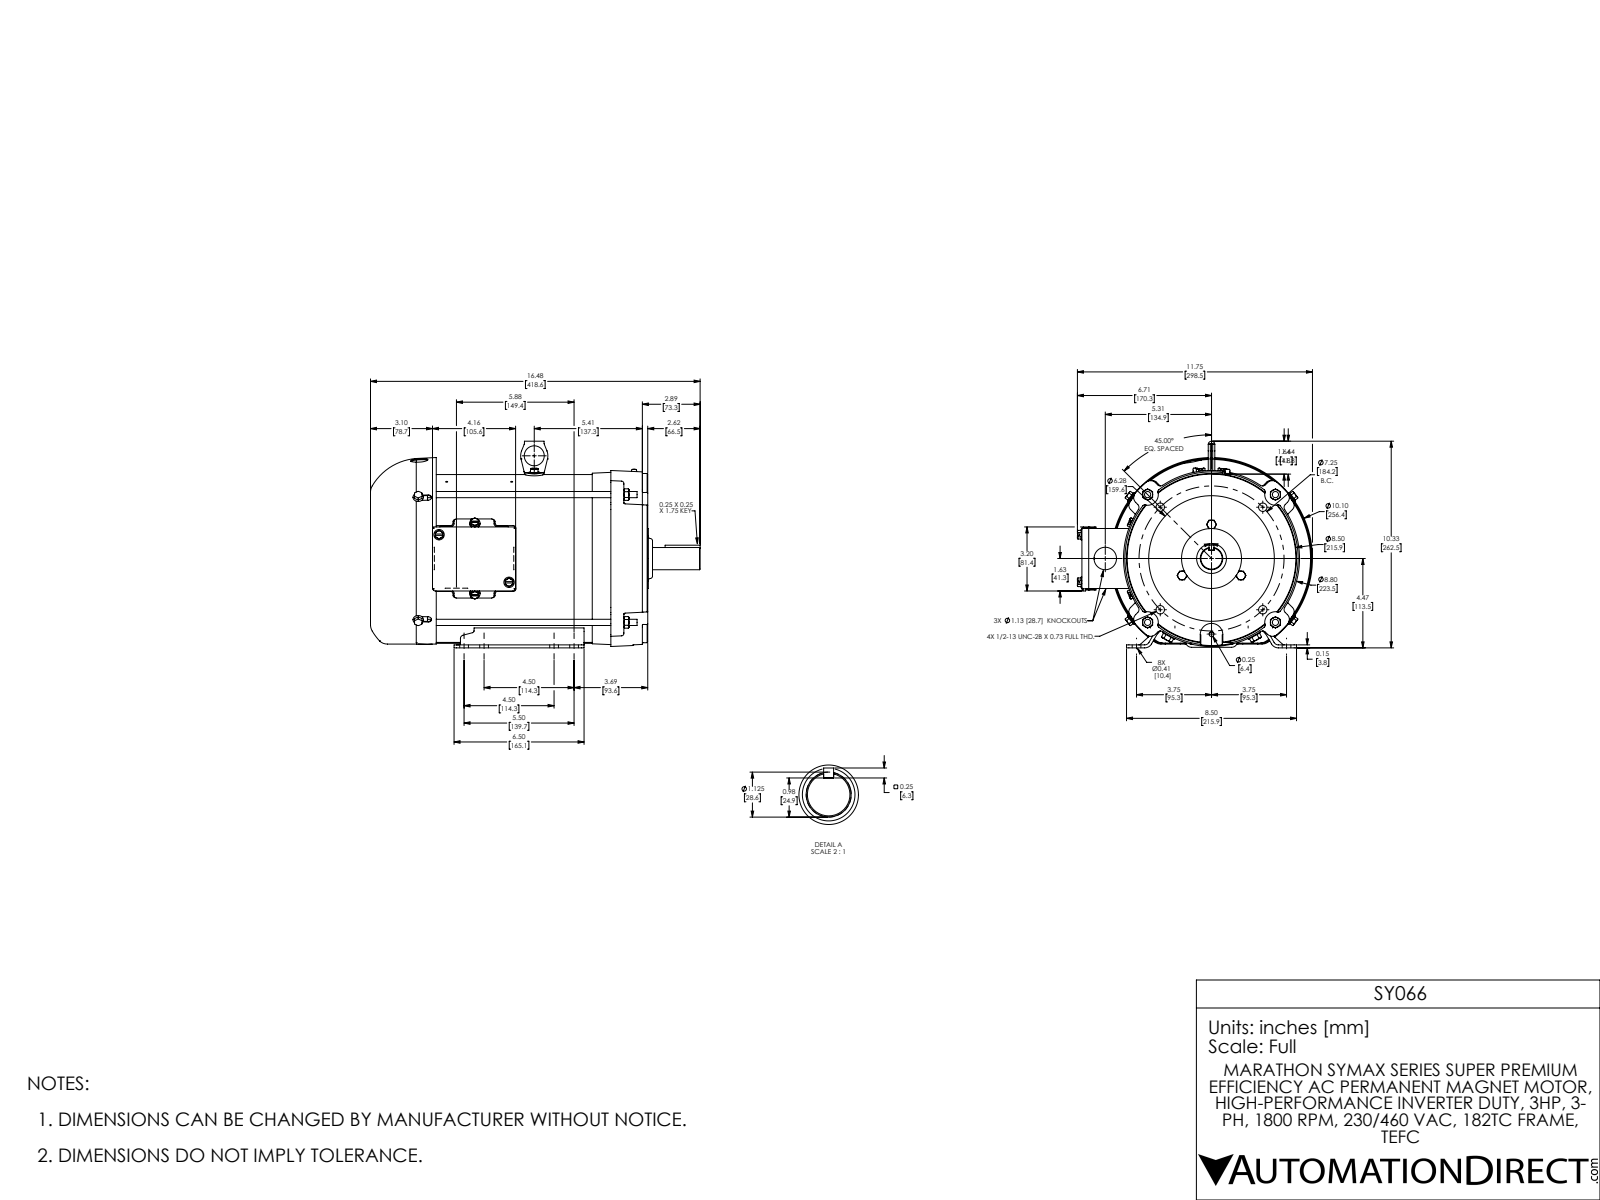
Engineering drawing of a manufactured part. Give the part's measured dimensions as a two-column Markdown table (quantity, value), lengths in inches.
| quantity | value |
| --- | --- |
| part name | 036316-800_RevA_182TC_3HP r1 Coord |
| STEP written by | SolidWorks 2017 (AUTOMOTIVE_DESIGN) |
| units | inches |
| bodies | 44 solids, 2571 faces (693 planar, 825 cylindrical, 1053 other) |
| overall size | 16.481 × 11.753 × 10.334 |
| volume | 155.7 in³ |
| surface area | 1 674 in² |
| round holes (diameter × count) | 0.38 × 8, 0.213 × 7, 0.276 × 6, 0.435 × 6, 0.104 × 4, 0.236 × 4, 0.257 × 4, 0.28 × 4, 0.344 × 4, 0.422 × 4, 0.281 × 3, 0.25 × 2 |
| round bosses / shafts (diameter × count) | 0.25 × 13, 0.676 × 6, 0.52 × 6, 0.313 × 6, 0.31 × 6, 0.522 × 4, 0.33 × 3, 0.309 × 2 |
| partial cylindrical surfaces (radius × count) | 0.125 × 64, 0.12 × 46, 0.13 × 20, 0.09 × 16, 0.19 × 16, 0.03 × 8, 0.165 × 8, 0.25 × 8 |
| main face-to-face distances | 0.048, 0.2, 0.15, 11.47, 11.27, 11.69, 11.49, 0.22, 12.115, 11.915 |
| hole center spacings | 5.793, 2.31, 0.893, 1, 2.315, 3.5, 3.625, 4.5 |
